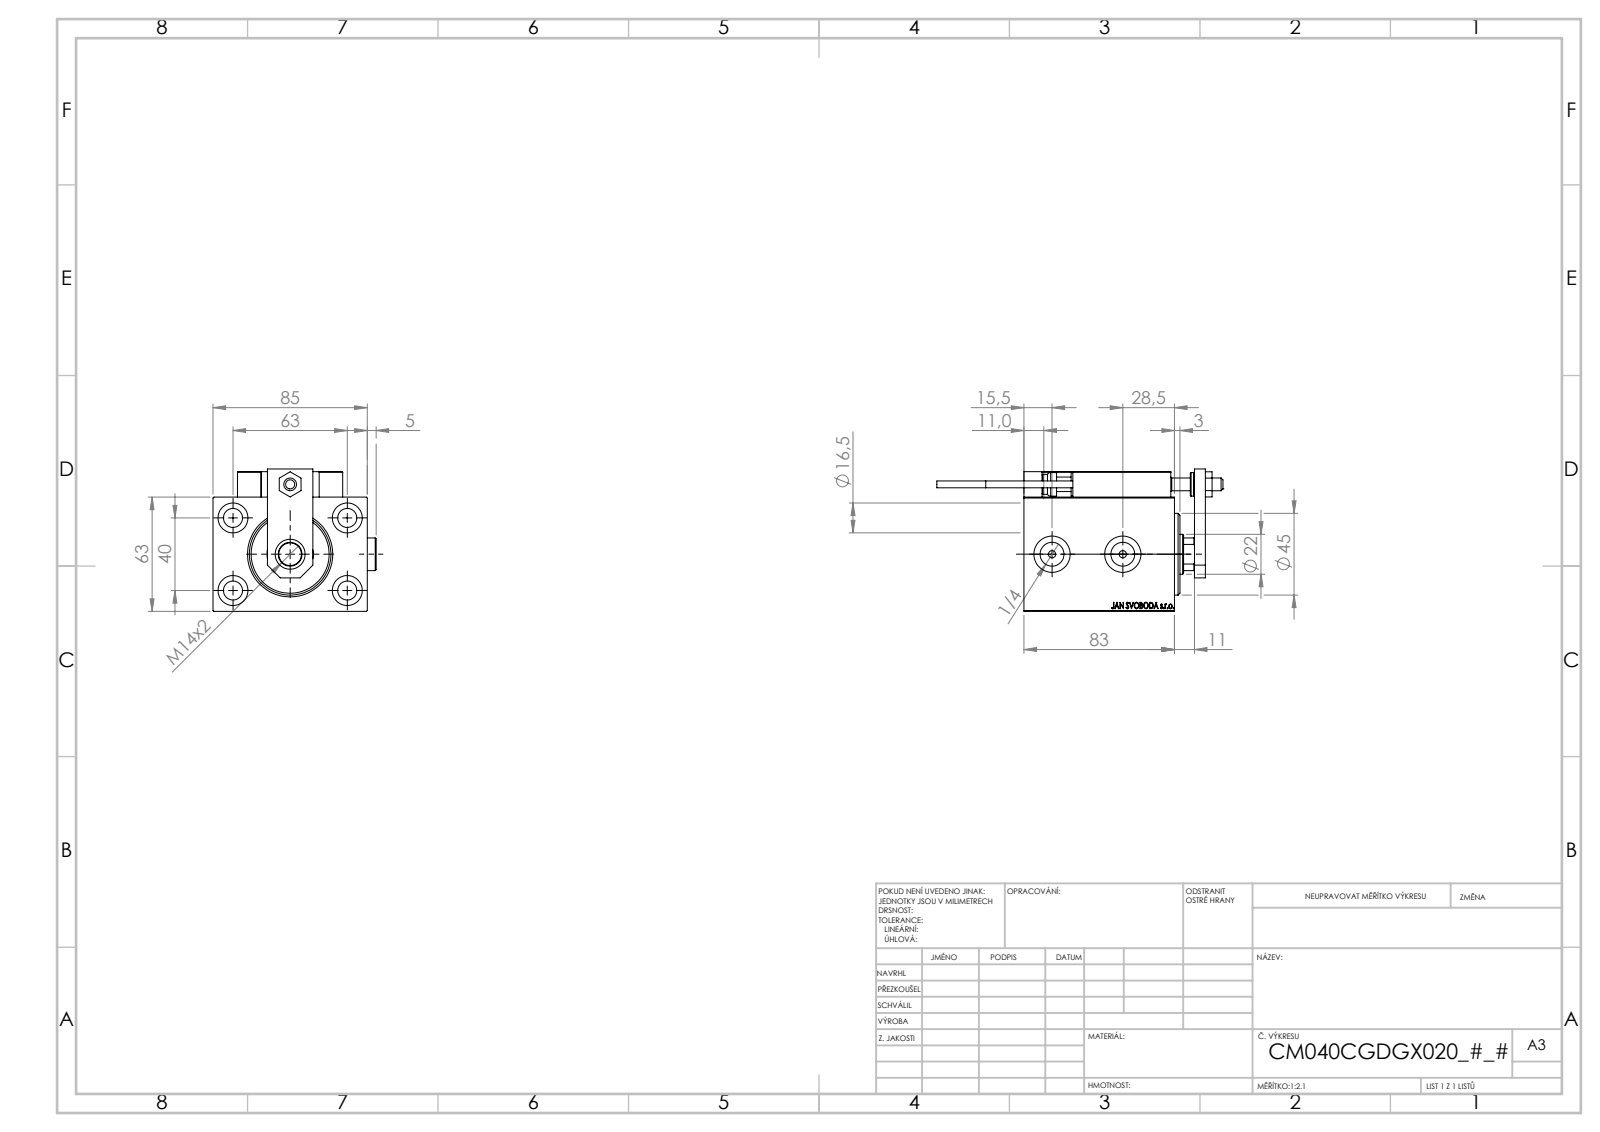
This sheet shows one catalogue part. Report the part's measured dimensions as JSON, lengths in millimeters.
{"part_name": "V450CM_C_Body; TYC_L79; V450CM_VC_B; ALLEN BOLT D5 (+7 more)", "step_written_by": "SolidWorks 2019 (CONFIG_CONTROL_DESIGN)", "units": "millimeters", "bodies": {"solids": 23, "faces": 1296, "planar": 564, "cylindrical": 198, "other": 534}, "overall_size": [157.7, 85, 78.5], "volume_mm3": 432085, "surface_area_mm2": 93464, "round_holes": [[4, 6], [8, 5], [16.5, 5], [3.2, 4], [10.5, 4], [5, 2], [13.16, 2], [20, 2], [7, 1], [12.5, 1], [22, 1], [25.5, 1]], "round_bosses_or_shafts": [[5, 2], [3.8, 2], [13, 1], [11, 1]], "partial_cylinders_radius": [[0.3, 30], [3, 2], [10.5, 1]], "face_to_face_distances": [63, 85, 14, 83, 38.5, 44.5, 18, 20, 10, 13], "hole_center_spacings": [37.31, 11.37, 20, 29.59, 29.69, 35.06, 36.06, 36.53]}
